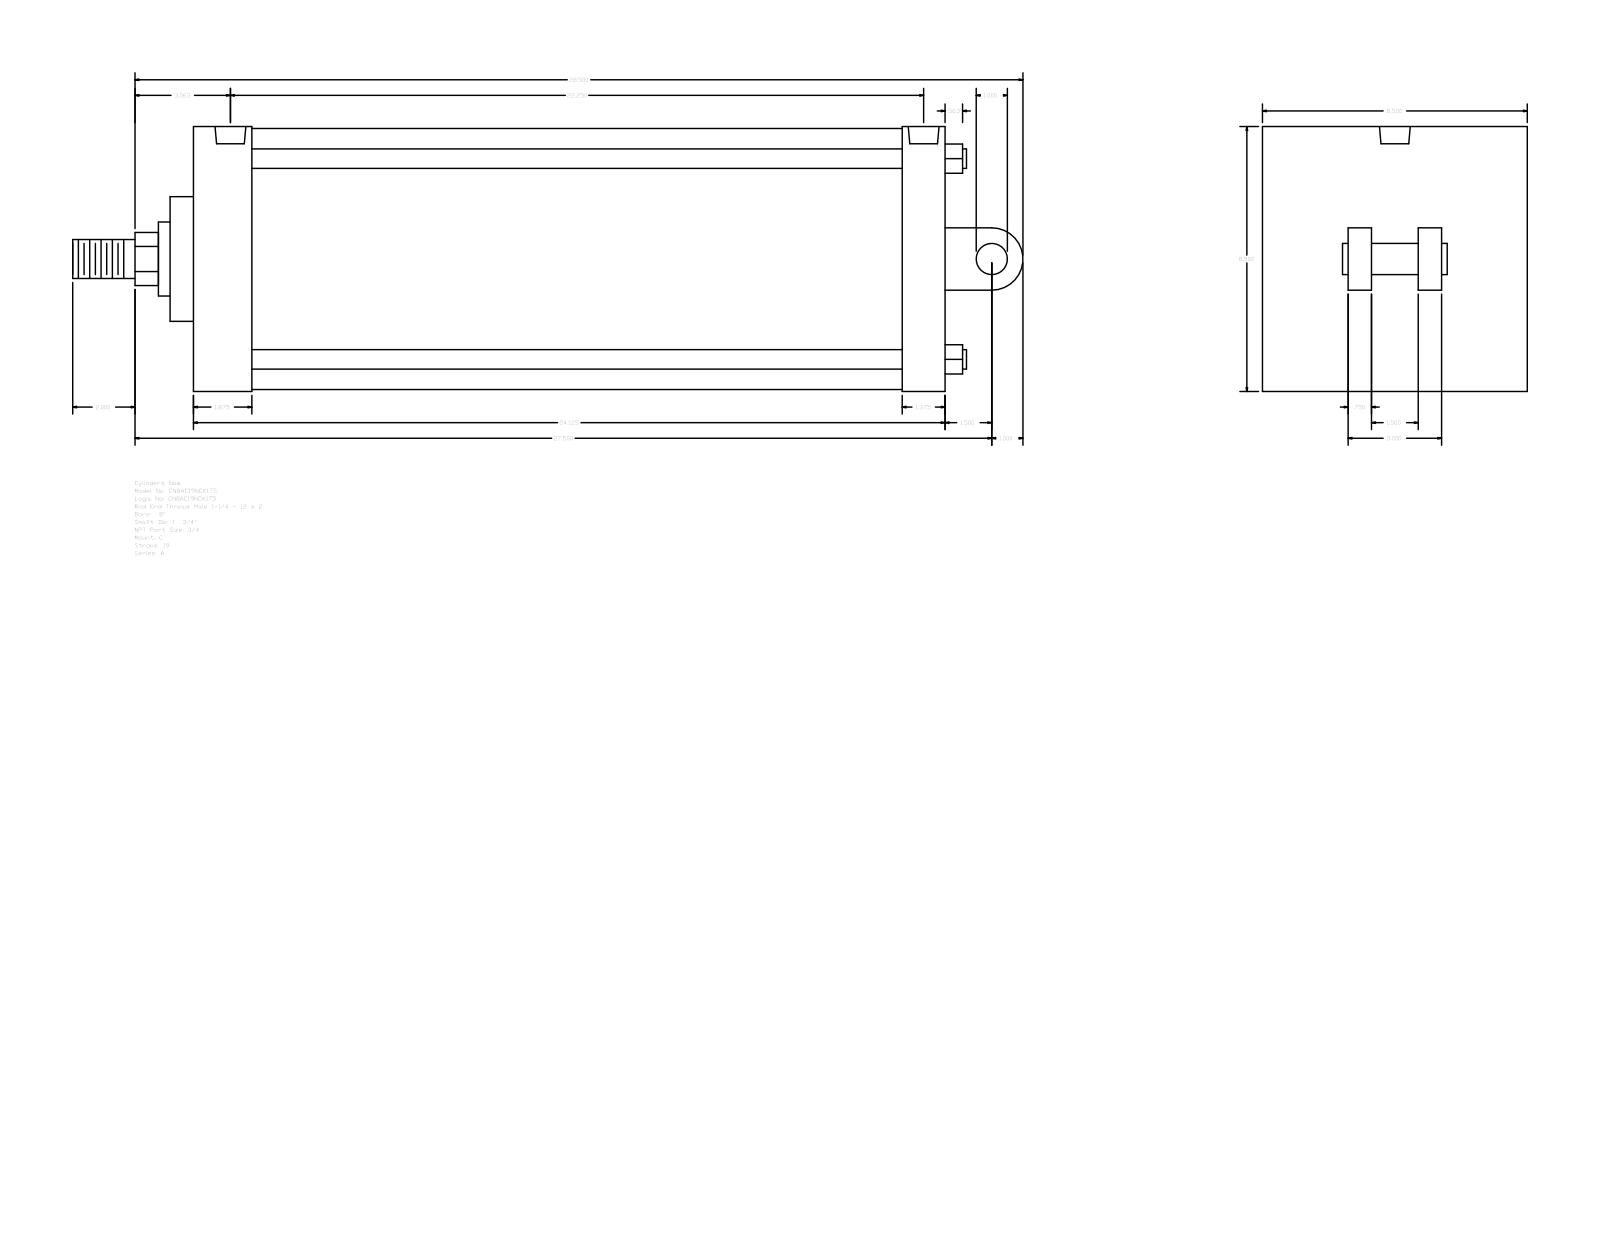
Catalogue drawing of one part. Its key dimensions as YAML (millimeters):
part_name: "A_C__0800_1.75"
step_written_by: "GSSL Pune (CONFIG_CONTROL_DESIGN)"
units: millimeters
bodies: {solids: 0, faces: 104, planar: 75, cylindrical: 29, other: 0}
overall_size: [774.7, 215.9, 215.9]
round_holes:
  - {diameter: 15.08, count: 4}
  - {diameter: 25.12, count: 2}
round_bosses_or_shafts:
  - {diameter: 15.88, count: 4}
  - {diameter: 212.72, count: 1}
  - {diameter: 60.33, count: 1}
  - {diameter: 44.45, count: 1}
  - {diameter: 31.75, count: 1}
  - {diameter: 25.4, count: 1}
partial_cylinders:
  - {radius: 21.63, count: 1}
  - {radius: 25.4, count: 1}
face_to_face_distances: [612.78, 215.9, 19.05, 57.15, 47.63, 565.15, 577.86, 530.23, 34.92, 69.85]
hole_center_spacings: [6.35, 552.45, 558.8, 565.15]
